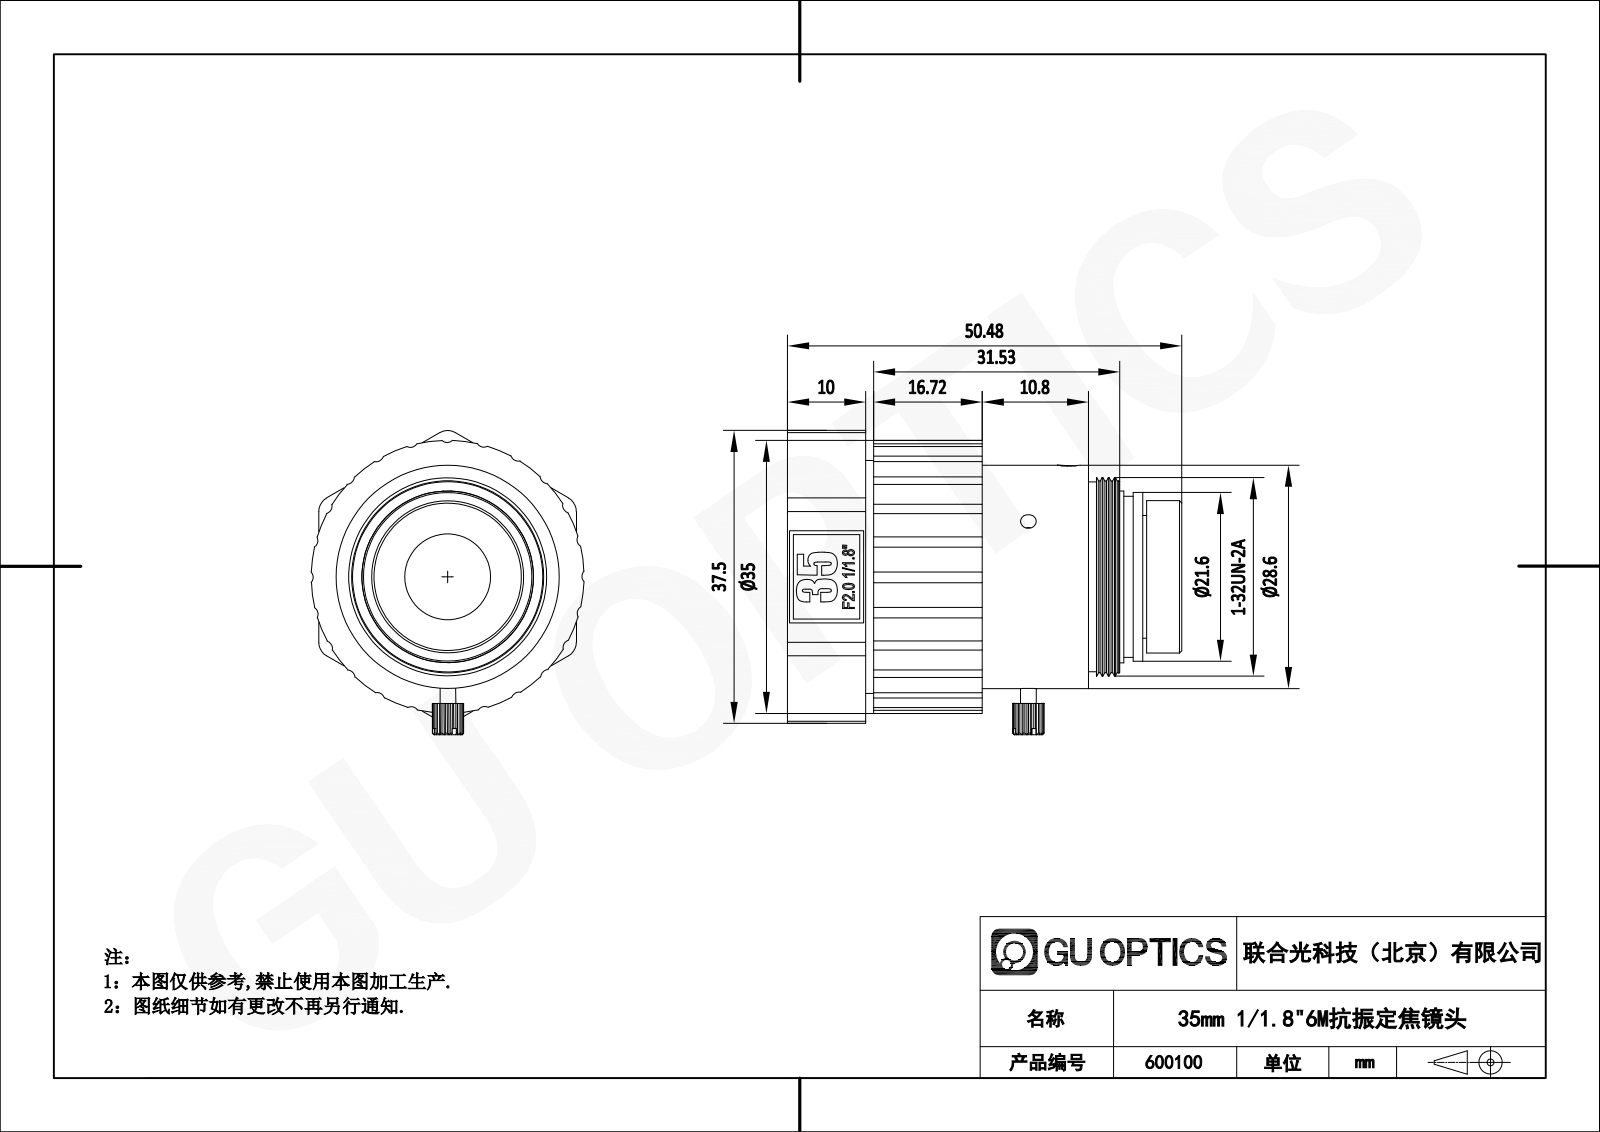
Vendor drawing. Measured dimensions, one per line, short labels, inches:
name: 600100
written by: SolidWorks 2020 (CONFIG_CONTROL_DESIGN)
unit: in
bodies: 4 solids, 395 faces (194 planar, 111 cylindrical, 90 other)
size: 1.987 × 1.533 × 1.376
volume: 1.751 in³; area: 23.3 in²
holes: 3× ⌀0.079, 1× ⌀0.067, 1× ⌀0.118, 1× ⌀0.433, 1× ⌀0.736, 1× ⌀0.866, 1× ⌀1.039, 1× ⌀1.087, 1× ⌀1.102, 1× ⌀1.181, 1× ⌀1.228, 1× ⌀1.236
bosses: 1× ⌀1.22, 1× ⌀1.173, 1× ⌀1.126, 1× ⌀1, 1× ⌀0.966, 1× ⌀0.957, 1× ⌀0.866, 1× ⌀0.85
rounds: 24× R0.039, 7× R0.079, 1× R0.689
face distances: 0.039, 1.299, 1.006, 0.548, 0.197, 0.177, 0.157, 0.981, 0.508, 0.575
hole spacings: 0.205
